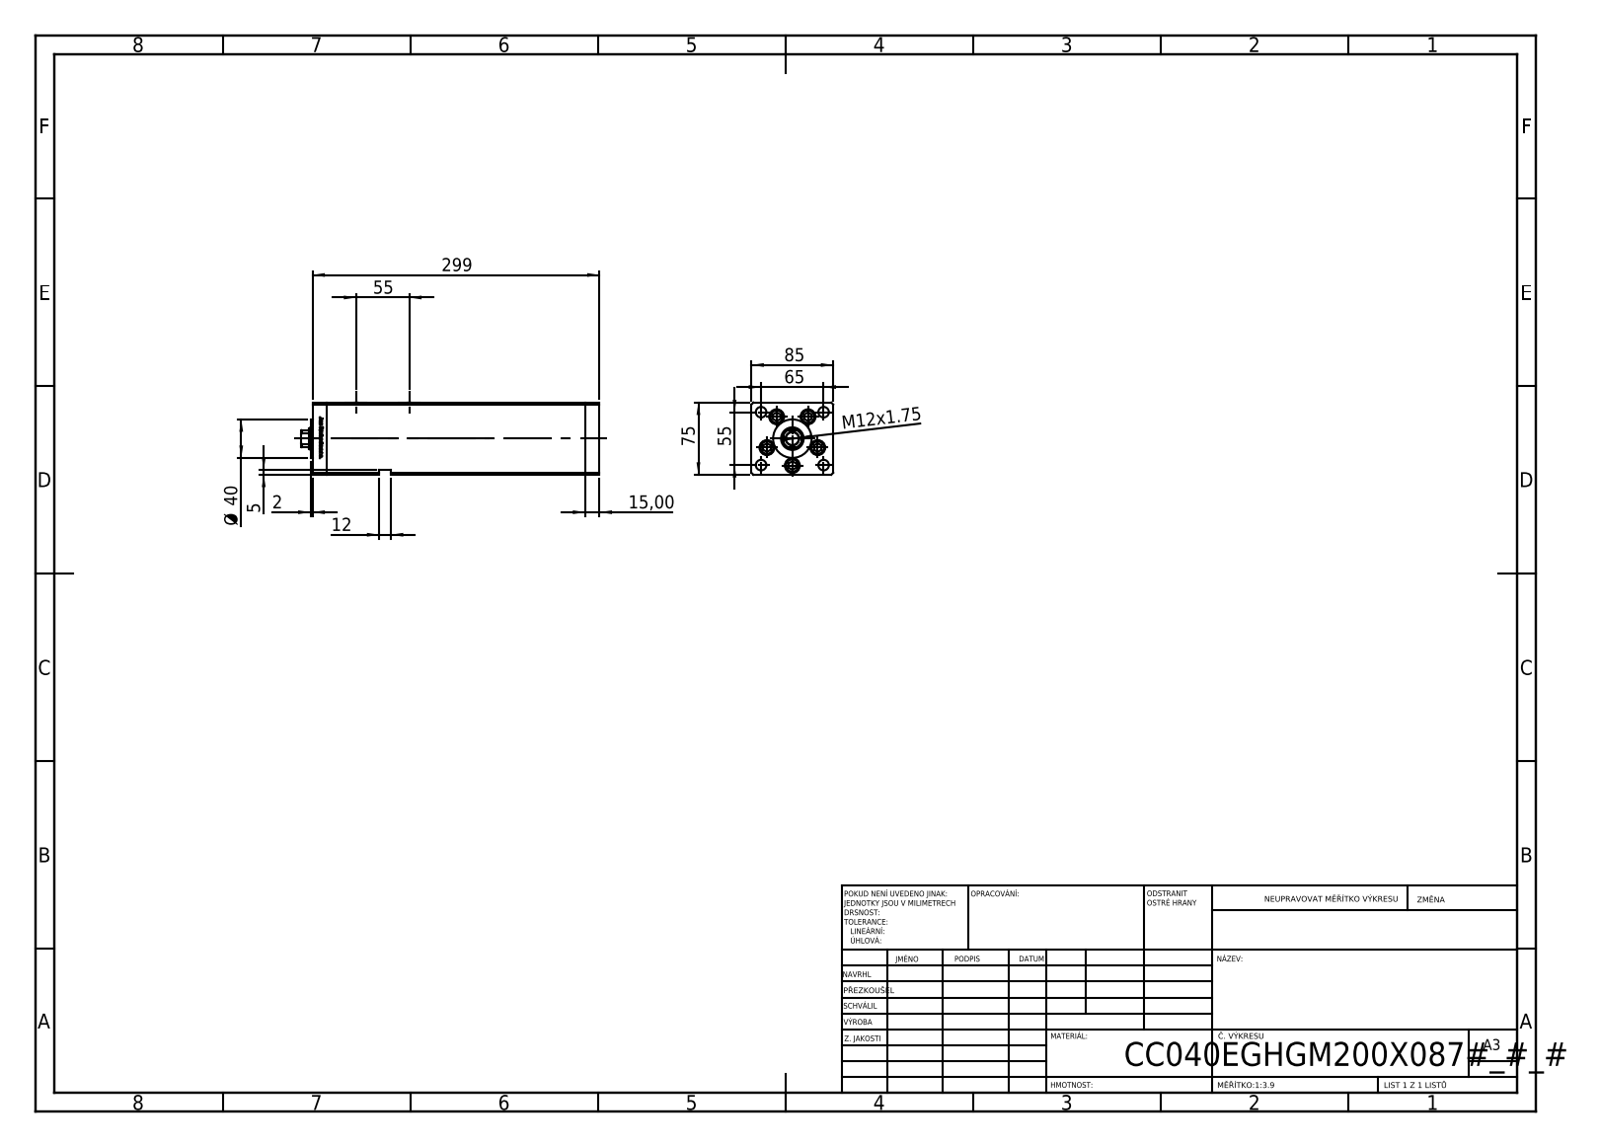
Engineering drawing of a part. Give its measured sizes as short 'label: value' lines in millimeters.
name: V220C_VC_E; ALLEN BOLT; V220C_FRONT_E; V220C_E MIDDLE (+1 more)
written by: SolidWorks 2019 (CONFIG_CONTROL_DESIGN)
unit: mm
bodies: 14 solids, 1212 faces (473 planar, 165 cylindrical, 574 other)
size: 310 × 85 × 75
volume: 1 606 000 mm³; area: 236 250 mm²
holes: 9× ⌀11, 5× ⌀15.5, 4× ⌀10.5, 4× ⌀16.5, 2× ⌀2, 2× ⌀13.16, 1× ⌀13.5, 1× ⌀22, 1× ⌀23.5
bosses: 5× ⌀14.5, 5× ⌀8, 1× ⌀40
rounds: 2× R0.93, 1× R10.5
face distances: 85, 75, 15, 268.5, 283.5, 10.5, 68.5, 298.5, 64.5, 31.25
hole spacings: 28, 42.57, 55, 65, 85.15, 16.86, 19.17, 32.33
